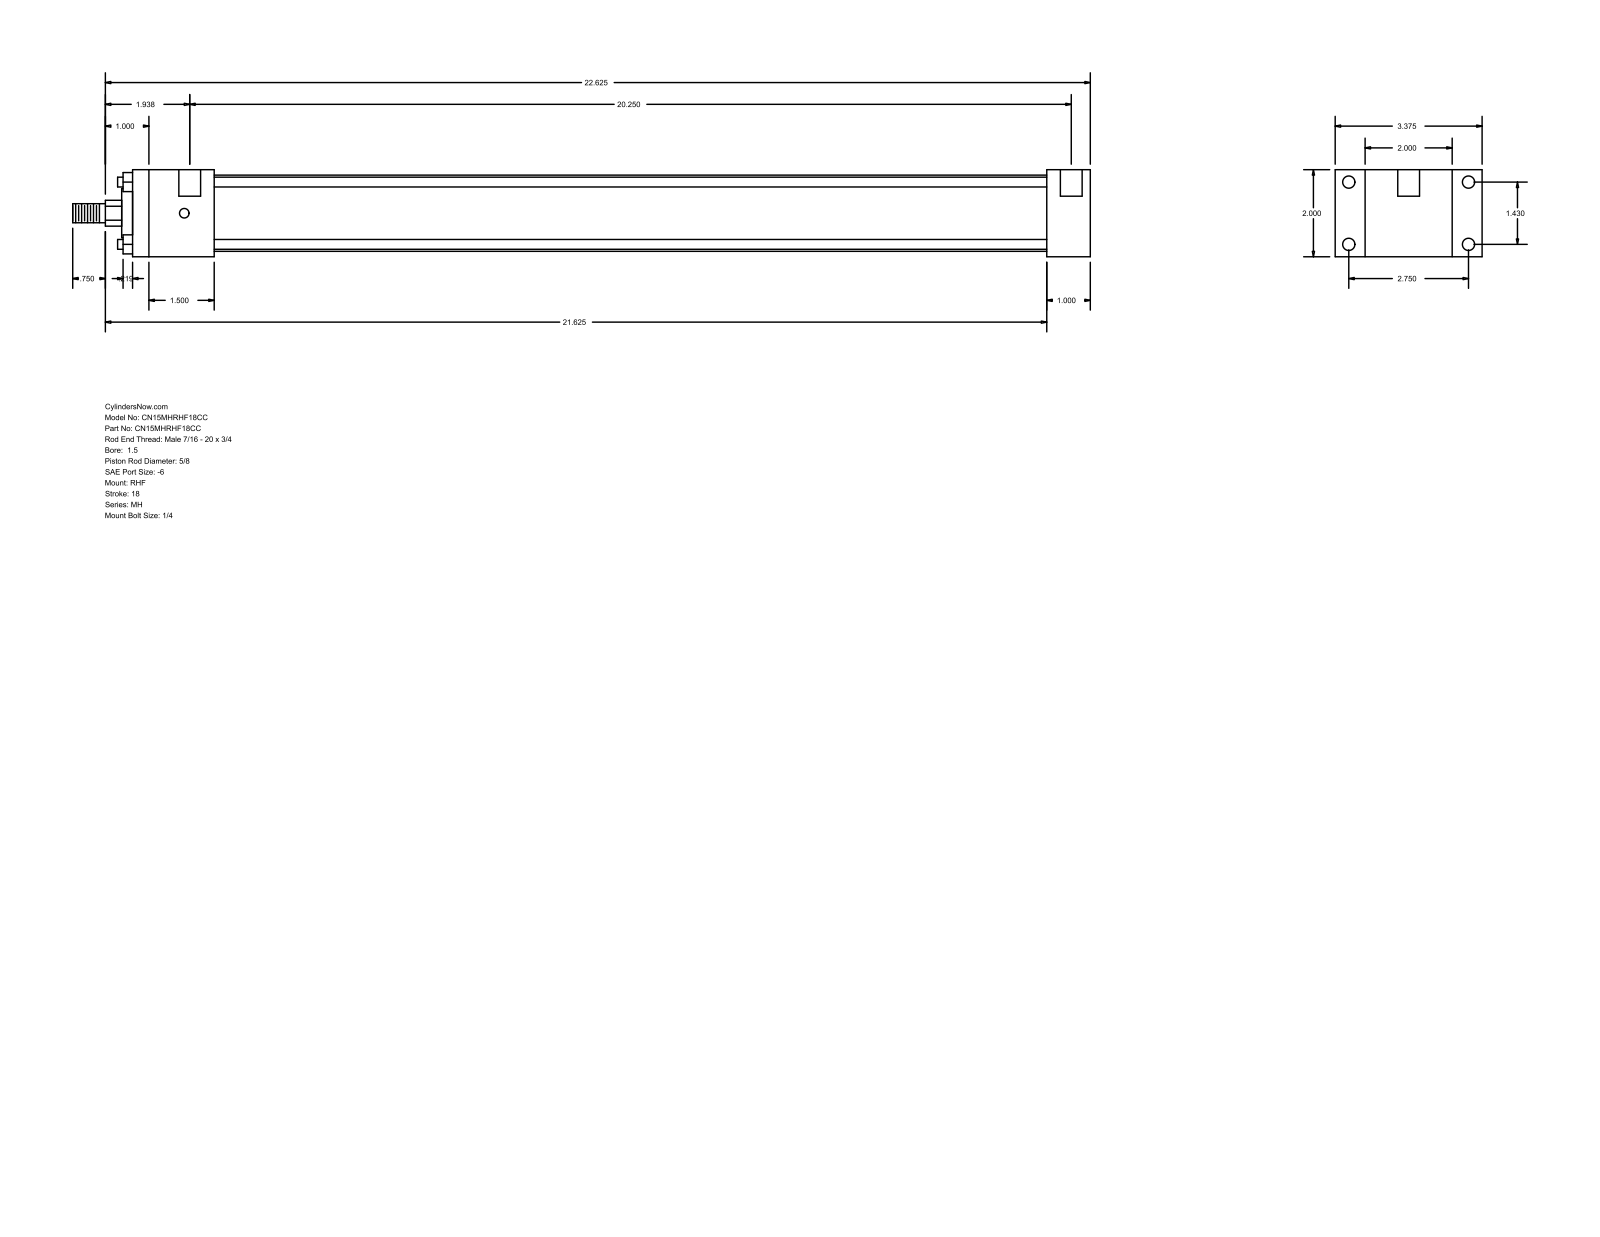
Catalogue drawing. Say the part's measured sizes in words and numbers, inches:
The part is named "MH_RHF__0150_0.625". Its 3-D file was written by "GSSL Pune (CONFIG_CONTROL_DESIGN)". It is 0 solids with 88 faces: 60 planar, 28 cylindrical and 0 other. Overall it measures 23.375 by 3.375 by 2 inches. Round holes: 4 of diameter 0.219, 4 of diameter 0.281, 2 of diameter 0.5. Round bosses or shafts: 4 of diameter 0.225, 1 of diameter 1.75, 1 of diameter 1.125, 1 of diameter 0.625, 1 of diameter 0.437. Partial cylindrical surfaces (rounded edges, fillets, slot ends): 1 of radius 0.297. The main face-to-face distances are 2, 1, 0.687, 2.687, 21, 22, 3.375, 1.875, 19.125, 20.125. The hole center spacings are 1.43, 2.75, 3.099, 20.375, 0.125, 20.25.
